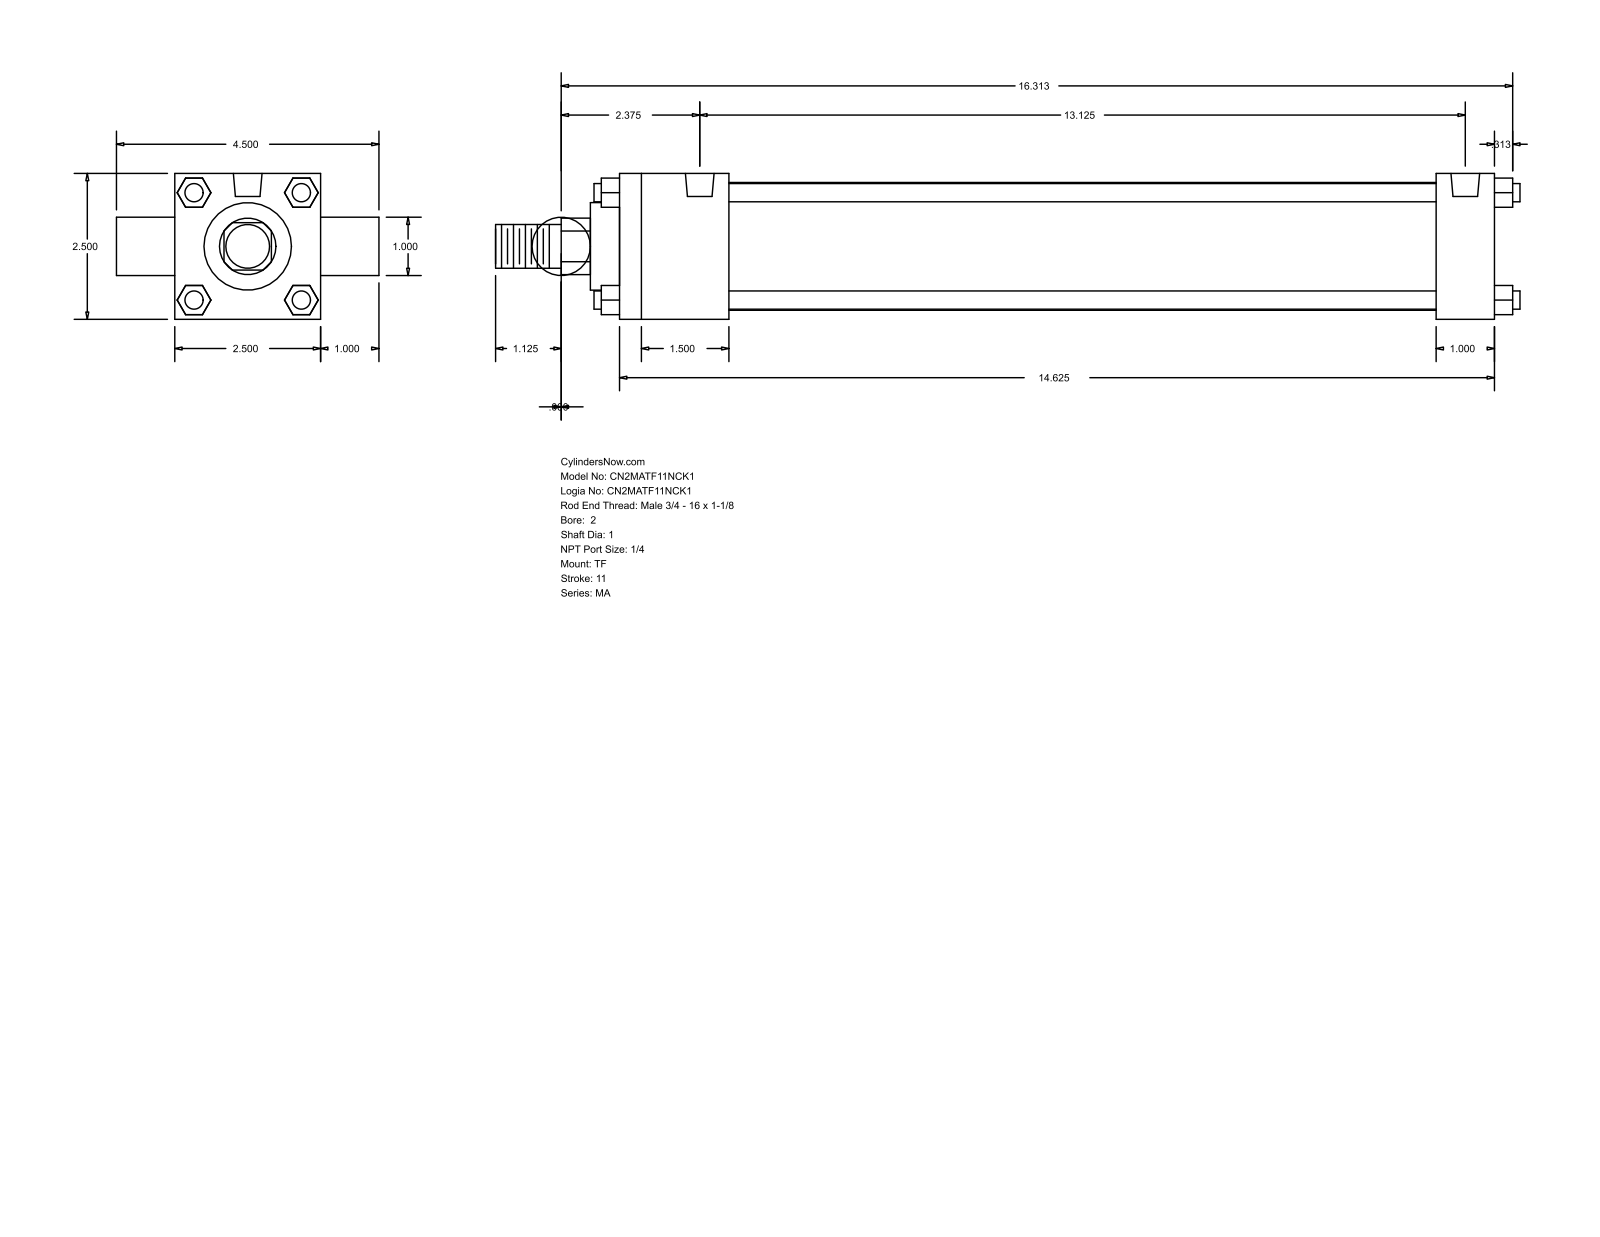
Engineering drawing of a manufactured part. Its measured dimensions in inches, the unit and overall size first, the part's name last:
Units: inches
Overall size (bounding box): 17.563 × 4.5 × 2.5
Round holes (diameter × count): ⌀0.313 ×3, ⌀0.492 ×2
Round bosses / shafts (diameter × count): ⌀0.313 ×4, ⌀1 ×2, ⌀2.19 ×1, ⌀1.5 ×1, ⌀0.75 ×1
Partial cylindrical surfaces — rounded edges, fillets, slot ends (radius × count): R0.484 ×1
Main face-to-face distances: 2.5, 1, 15, 0.5, 1.875, 14, 12.125, 13.125, 3.5, 0.92
Hole centre spacings: 13.125
Bodies: 0 solids, 120 faces (92 planar, 28 cylindrical, 0 other)
Part name (STEP PRODUCT): MA_TF__0200_1
STEP written by: GSSL Pune (CONFIG_CONTROL_DESIGN)
